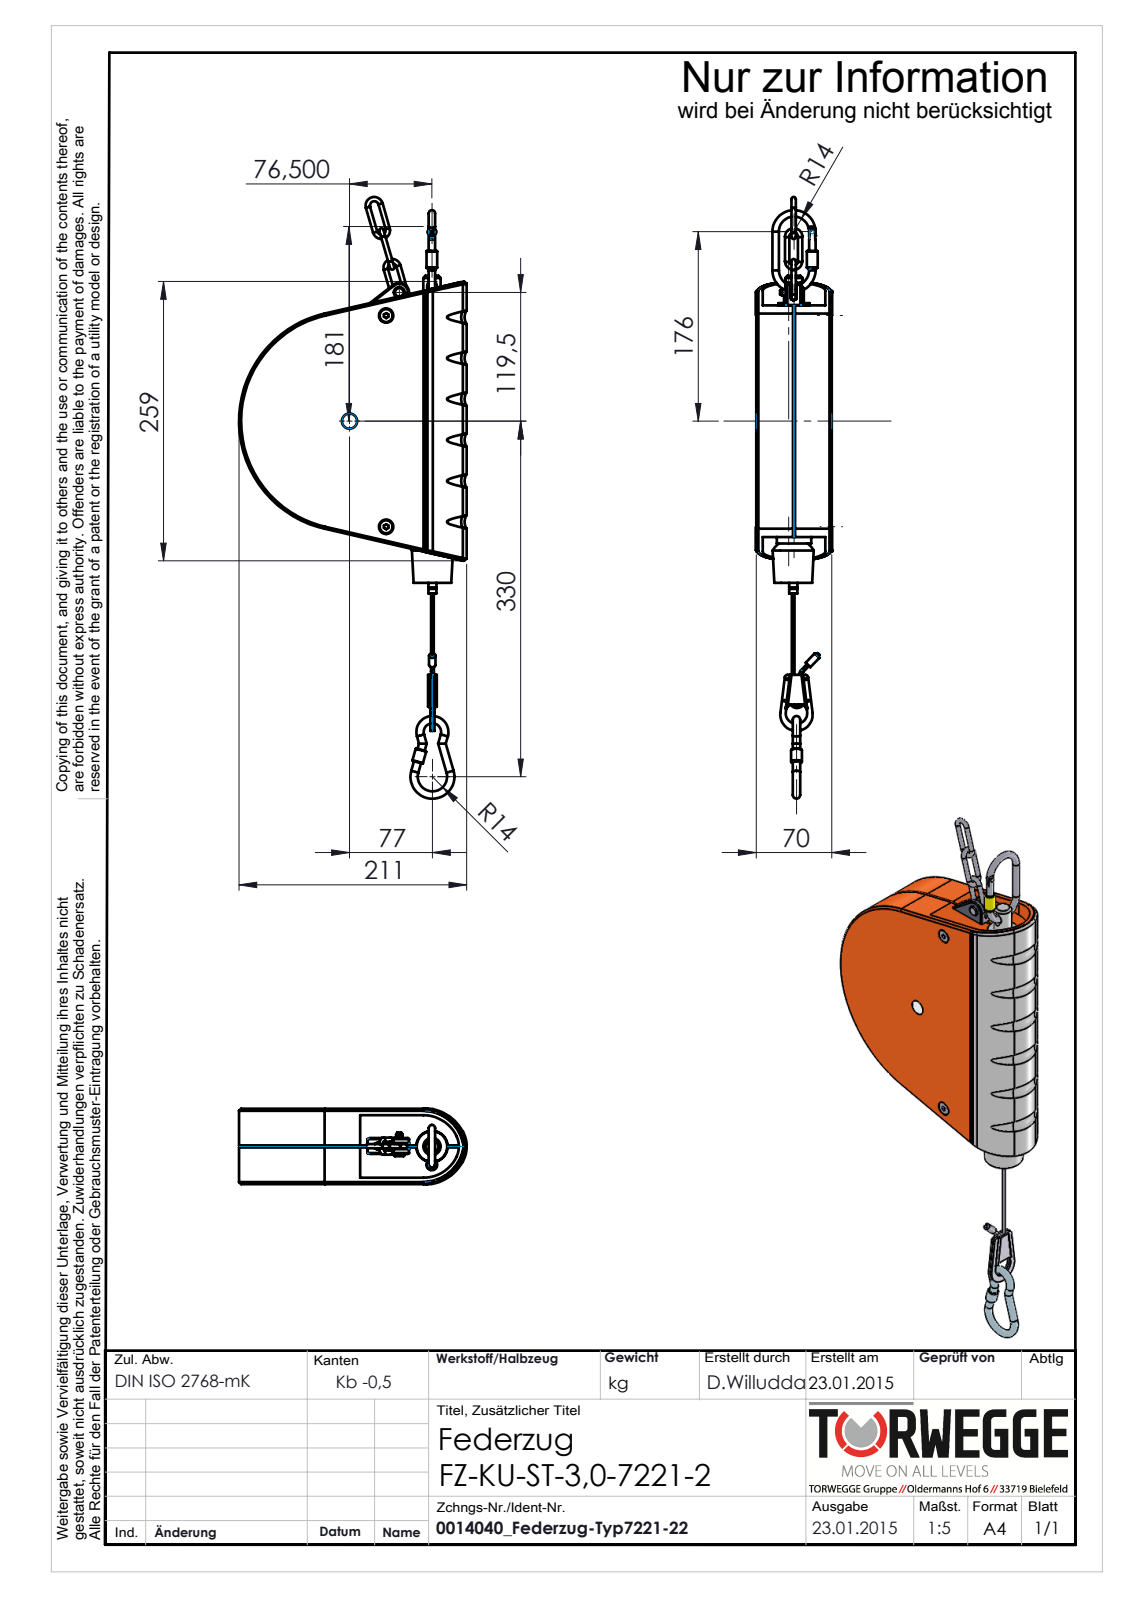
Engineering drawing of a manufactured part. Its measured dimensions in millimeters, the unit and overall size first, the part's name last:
Units: millimetres
Overall size (bounding box): 558.51 × 211.25 × 70.17
Round holes (diameter × count): ⌀1.6 ×1, ⌀6.8 ×1, ⌀7 ×1, ⌀8 ×1, ⌀14.1 ×1, ⌀20 ×1
Round bosses / shafts (diameter × count): ⌀4 ×6, ⌀6.8 ×4, ⌀6 ×4, ⌀10 ×3, ⌀12 ×2, ⌀32 ×1, ⌀29 ×1, ⌀16 ×1
Partial cylindrical surfaces — rounded edges, fillets, slot ends (radius × count): R1.5 ×8, R2 ×4, R0.2 ×2, R2.5 ×2, R20 ×2, R34 ×2, R38.5 ×2, R40 ×2
Main face-to-face distances: 70, 215, 6, 64, 2, 4, 42.5, 257.5, 36, 28
Hole centre spacings: 40.38, 146.47
Bodies: 0 solids, 466 faces (160 planar, 149 cylindrical, 157 other)
Part name (STEP PRODUCT): 0014040_Federzug-Typ7221-22
STEP written by: SolidWorks 2014 (AUTOMOTIVE_DESIGN)
